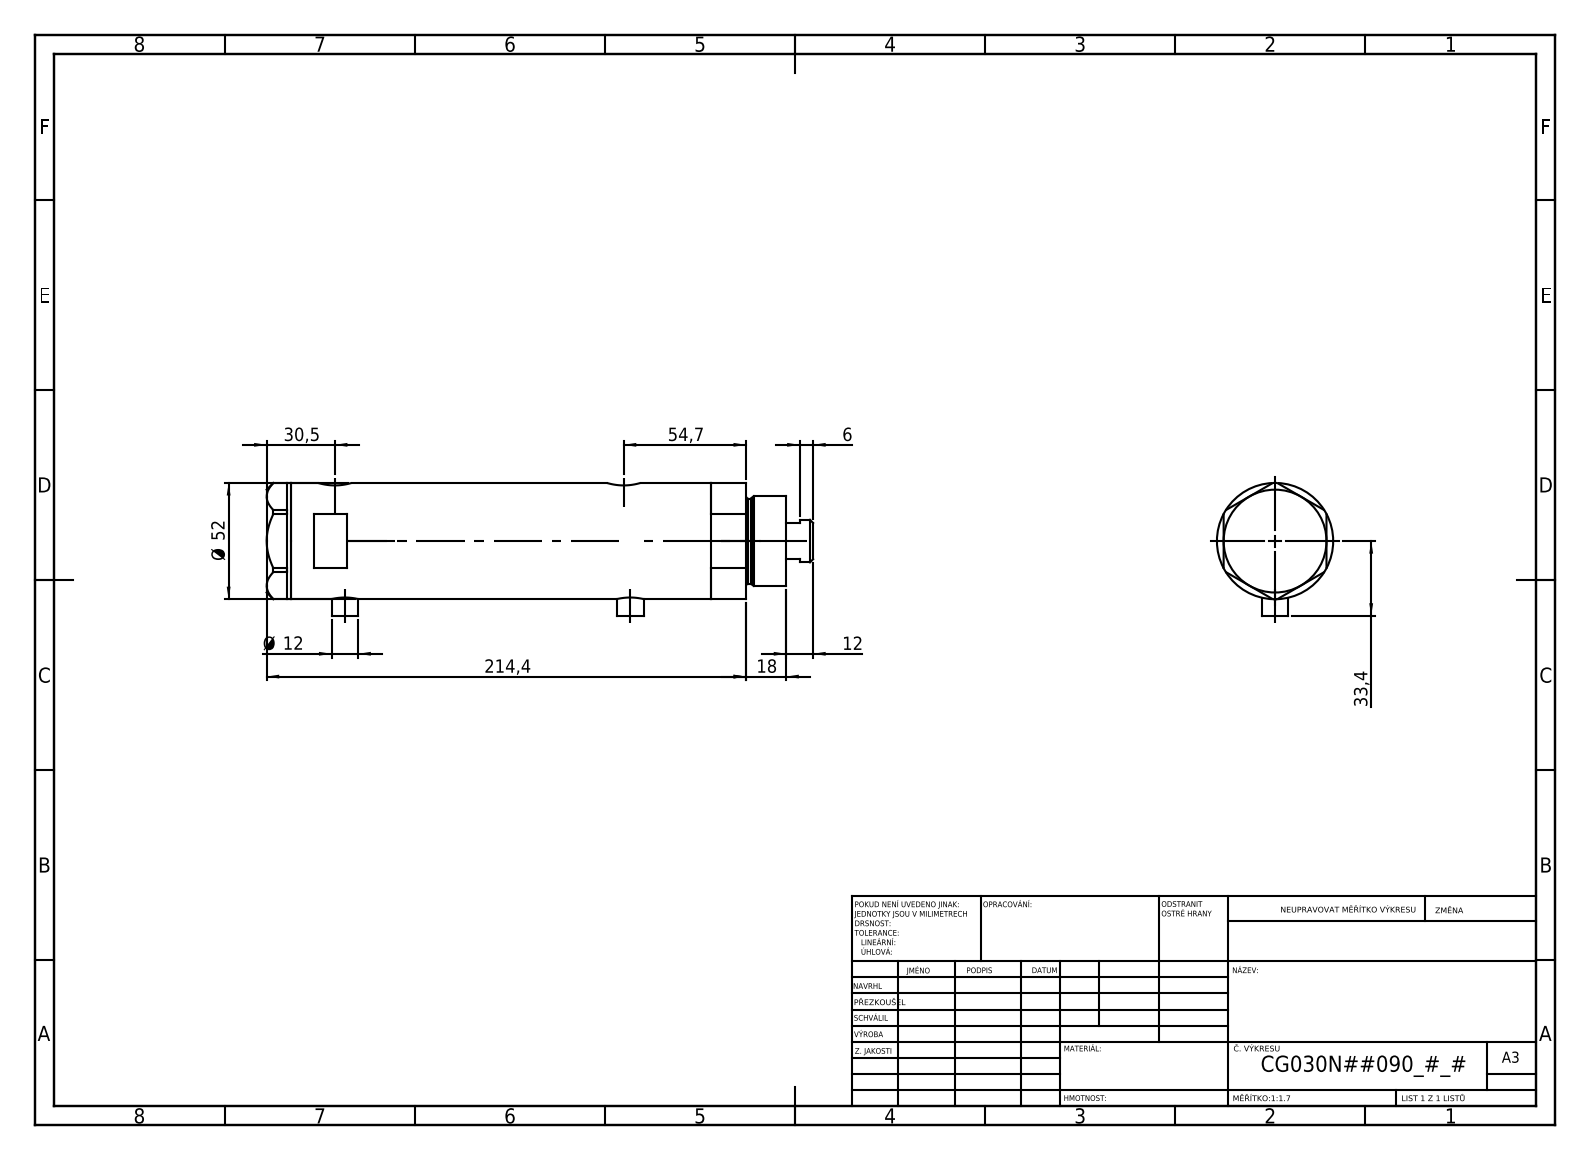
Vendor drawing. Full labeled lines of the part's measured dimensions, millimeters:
Part name (STEP PRODUCT): V270CG_VC; V270CG_MIDDLE; V270CG_FRONT; V270CG_BACK
STEP written by: SolidWorks 2019 (CONFIG_CONTROL_DESIGN)
Units: millimetres
Bodies: 4 solids, 134 faces (65 planar, 49 cylindrical, 20 other)
Overall size (bounding box): 244.4 × 59.4 × 52
Volume: 438 781 mm³ · Surface area: 96 361 mm²
Round holes (diameter × count): ⌀9.73 ×2, ⌀12.5 ×2, ⌀15 ×2, ⌀6.5 ×1, ⌀20 ×1, ⌀21.5 ×1, ⌀30 ×1, ⌀33 ×1, ⌀44 ×1
Round bosses / shafts (diameter × count): ⌀12 ×2, ⌀52 ×1, ⌀40 ×1, ⌀38 ×1, ⌀19 ×1
Main face-to-face distances: 151.5, 23.8, 127.7, 11, 34.8, 162.5, 46, 198.9, 187.9, 164.1
Hole centre spacings: 2.9, 4.5, 124.7, 127.6, 129.2, 132.1
